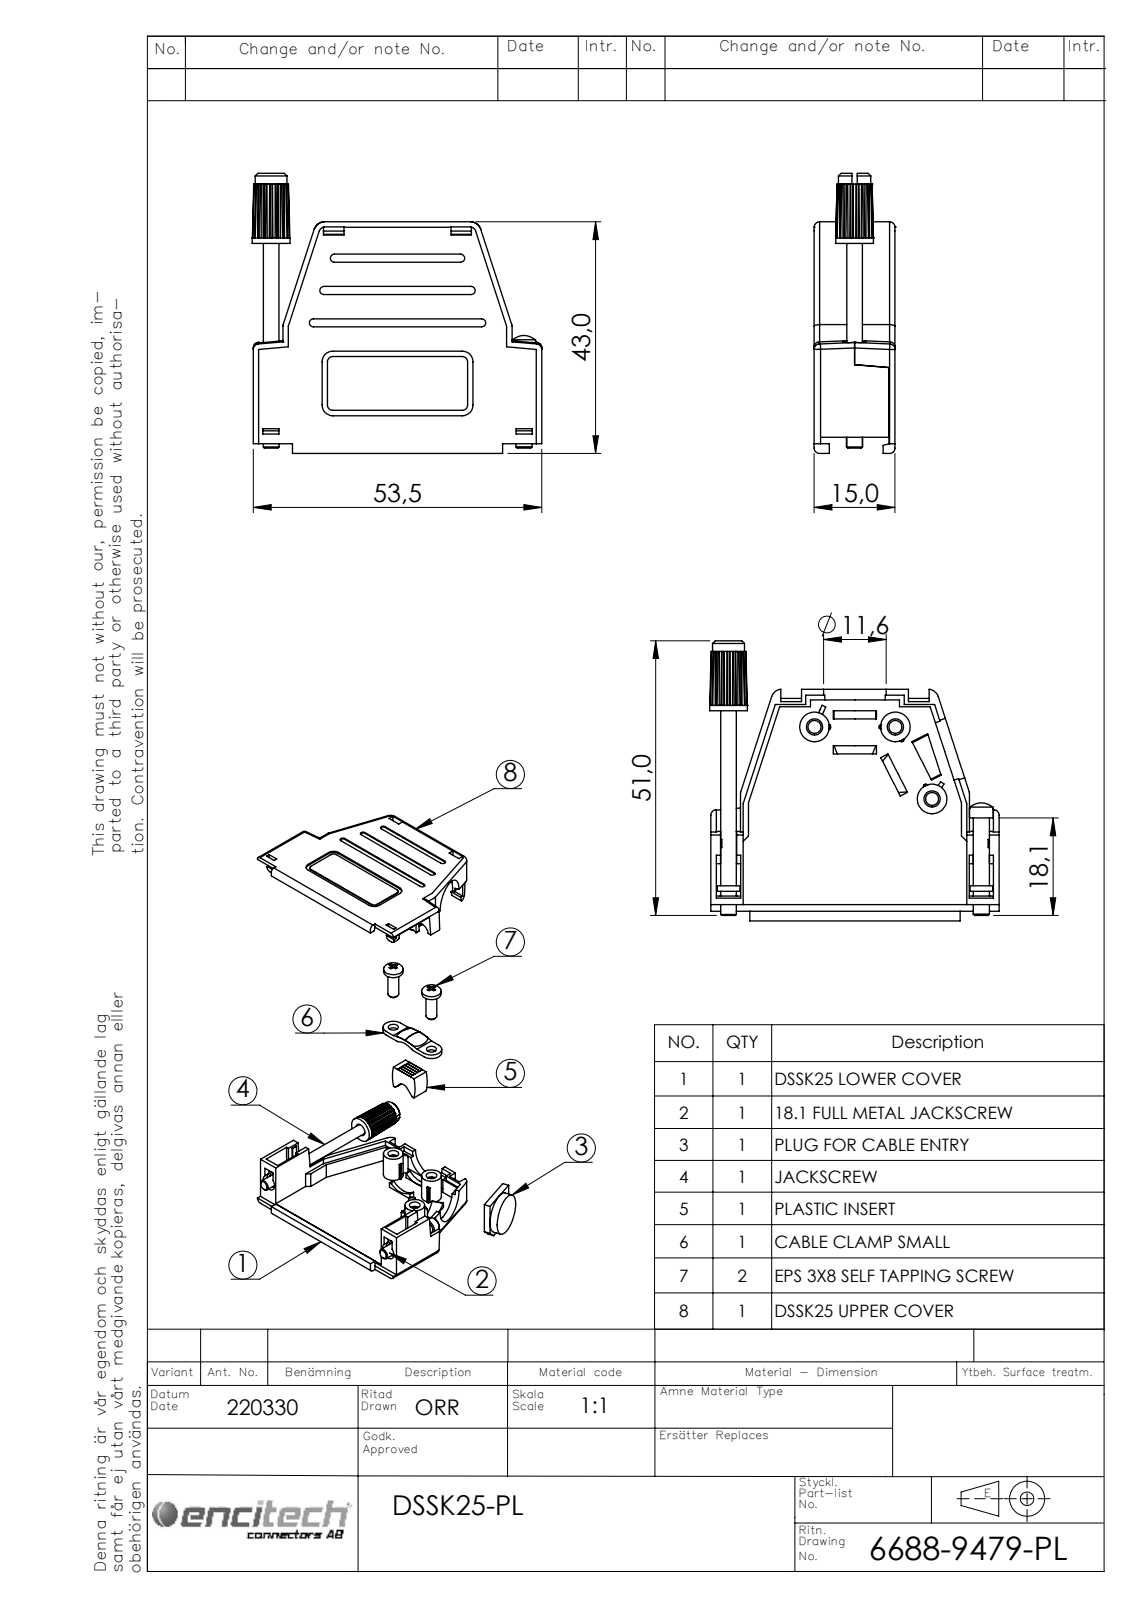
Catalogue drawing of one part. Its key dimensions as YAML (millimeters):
part_name: "6826-0133-01; 6838-0109-01; 6811-0132-11 Part 1; 6718-0101-01 (+5 more)"
step_written_by: "SolidWorks 2021 (AUTOMOTIVE_DESIGN)"
units: millimeters
bodies: {solids: 11, faces: 858, planar: 599, cylindrical: 181, other: 78}
overall_size: [53.7, 52, 15]
volume: 10952
surface_area: 15626
round_holes:
  - {diameter: 2.4, count: 3}
  - {diameter: 3, count: 3}
  - {diameter: 2.8, count: 2}
  - {diameter: 11.6, count: 2}
  - {diameter: 3.5, count: 1}
  - {diameter: 9.4, count: 1}
round_bosses_or_shafts:
  - {diameter: 5.5, count: 3}
  - {diameter: 5.45, count: 2}
  - {diameter: 4.2, count: 2}
  - {diameter: 11.4, count: 1}
  - {diameter: 7, count: 1}
  - {diameter: 6, count: 1}
  - {diameter: 4.4, count: 1}
  - {diameter: 3, count: 1}
partial_cylinders:
  - {radius: 1, count: 40}
  - {radius: 2, count: 14}
  - {radius: 0.75, count: 6}
  - {radius: 5.8, count: 5}
  - {radius: 0.1, count: 4}
  - {radius: 0.25, count: 4}
  - {radius: 0.5, count: 4}
  - {radius: 1.5, count: 3}
face_to_face_distances: [1.7, 13.3, 11.6, 15, 1.5, 2, 14.8, 13.1, 1.1, 5.8]
hole_center_spacings: [7.57, 15, 18.92, 25.58]
